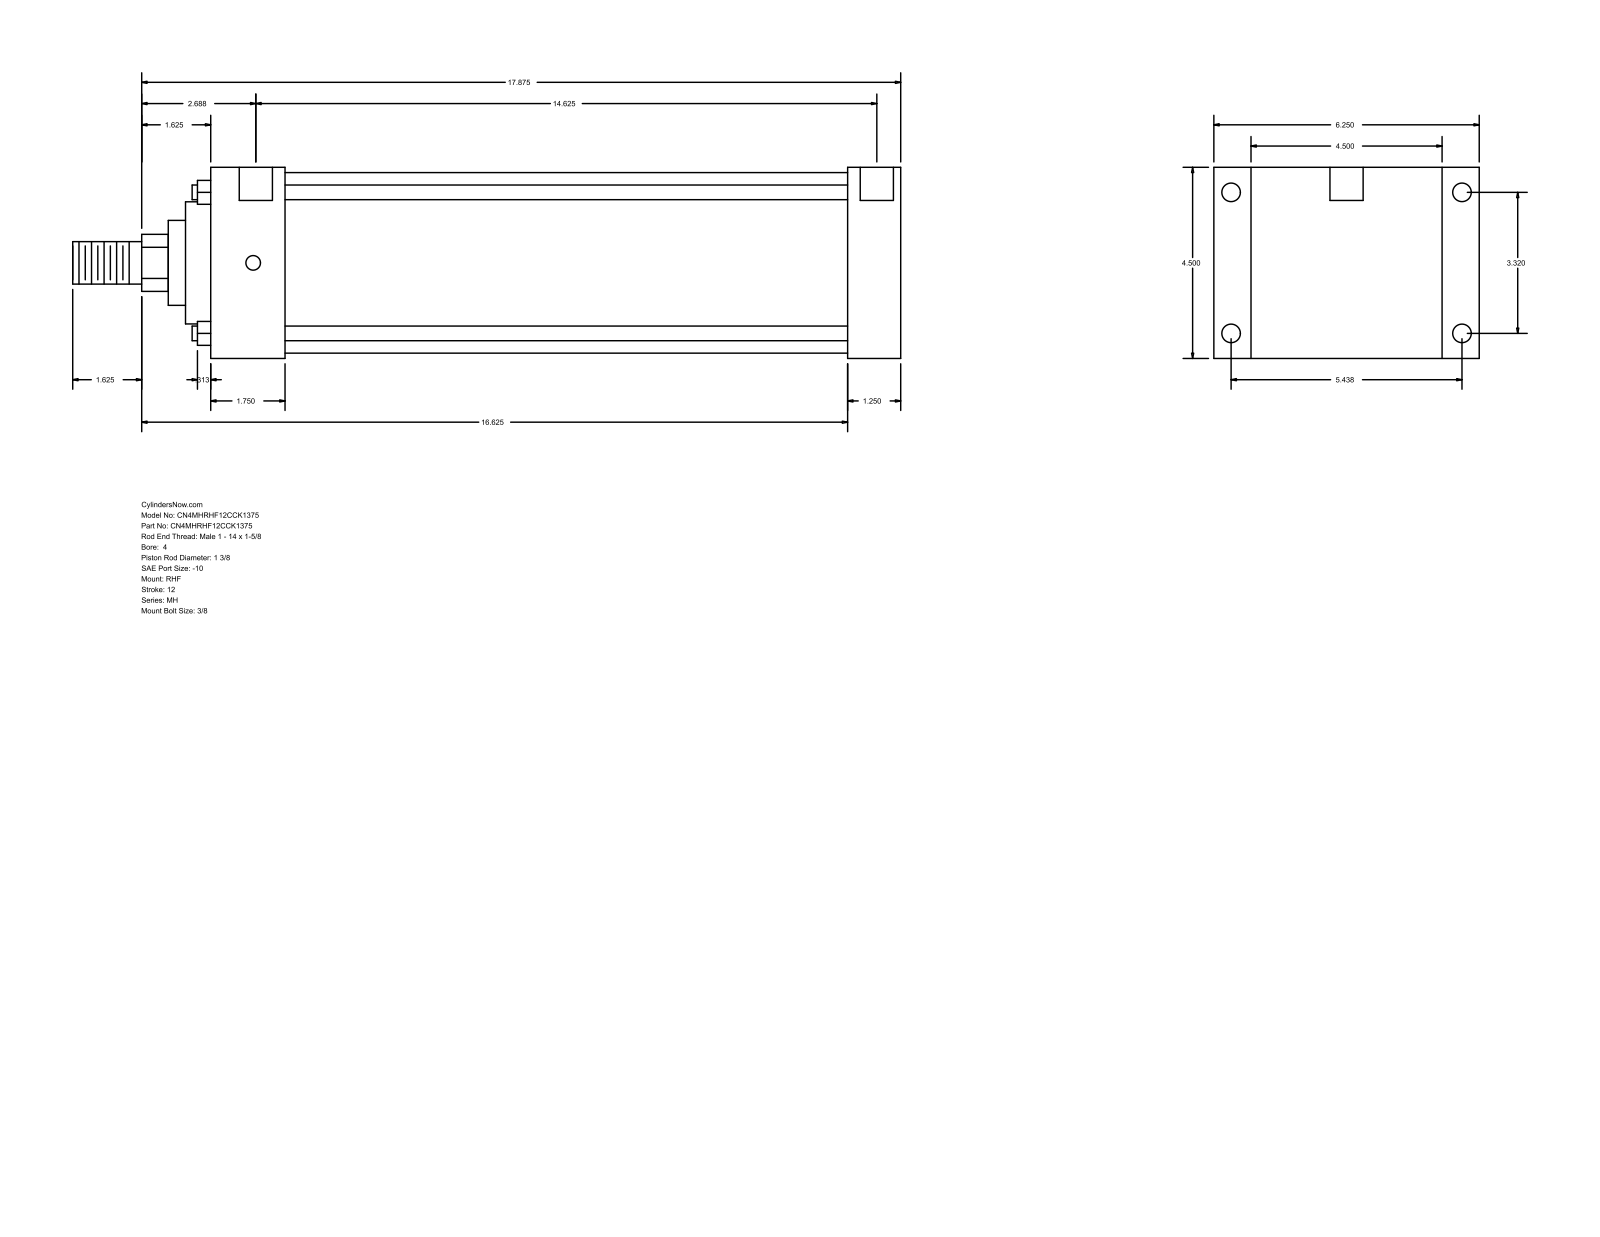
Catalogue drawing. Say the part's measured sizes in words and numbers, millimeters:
The part is named "MH_RHF__0400_1.375". Its 3-D file was written by "GSSL Pune (CONFIG_CONTROL_DESIGN)". It is 0 solids with 90 faces: 61 planar, 29 cylindrical and 0 other. Overall it measures 495.3 by 158.75 by 114.3 millimeters. Round holes: 4 of diameter 8.73, 4 of diameter 11.13, 2 of diameter 19.84. Round bosses or shafts: 4 of diameter 8.76, 1 of diameter 107.95, 1 of diameter 73.03, 1 of diameter 50.8, 1 of diameter 34.92, 1 of diameter 25.4. Partial cylindrical surfaces (rounded edges, fillets, slot ends): 1 of radius 17.06. The main face-to-face distances are 114.3, 31.75, 381, 412.75, 22.23, 136.53, 44.45, 336.55, 368.3, 158.76. The hole center spacings are 84.32, 138.12, 161.82, 374.65, 1.58, 1.59, 371.48, 373.06.
